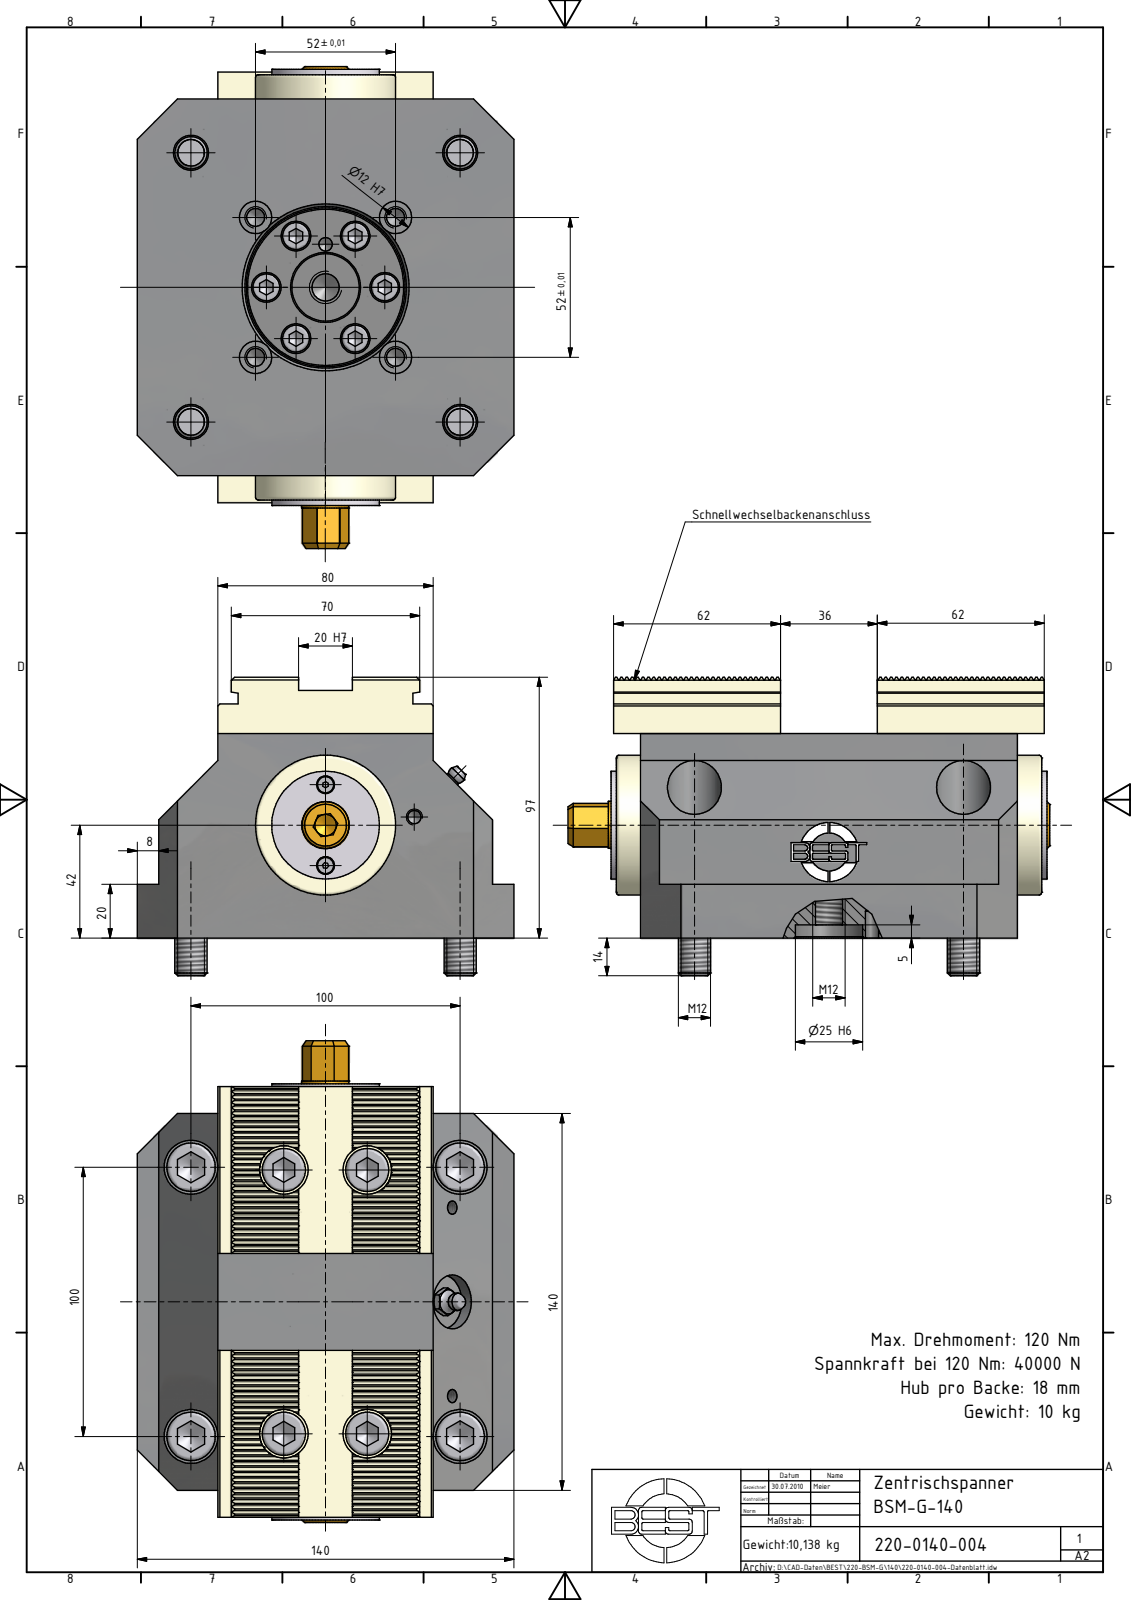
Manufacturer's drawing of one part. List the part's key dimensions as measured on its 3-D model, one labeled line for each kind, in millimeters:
Part name (STEP PRODUCT): 220-0140-004-Kunde
STEP written by: Autodesk Inventor 2010 (CONFIG_CONTROL_DESIGN)
Units: millimetres
Bodies: 1 solid, 329 faces (192 planar, 52 cylindrical, 85 other)
Overall size (bounding box): 179 × 140 × 111
Volume: 1 416 000 mm³ · Surface area: 122 410 mm²
Round holes (diameter × count): ⌀17.5 ×1
Round bosses / shafts (diameter × count): ⌀18 ×4, ⌀12 ×4, ⌀17.5 ×2, ⌀59 ×1, ⌀52 ×1, ⌀40 ×1, ⌀4 ×1
Partial cylindrical surfaces — rounded edges, fillets, slot ends (radius × count): R0.35 ×12, R0.88 ×8, R1.1 ×2, R1.98 ×2, R7.04 ×1, R11 ×1
Main face-to-face distances: 97, 140, 30, 22, 102, 76, 21, 110, 52, 8
